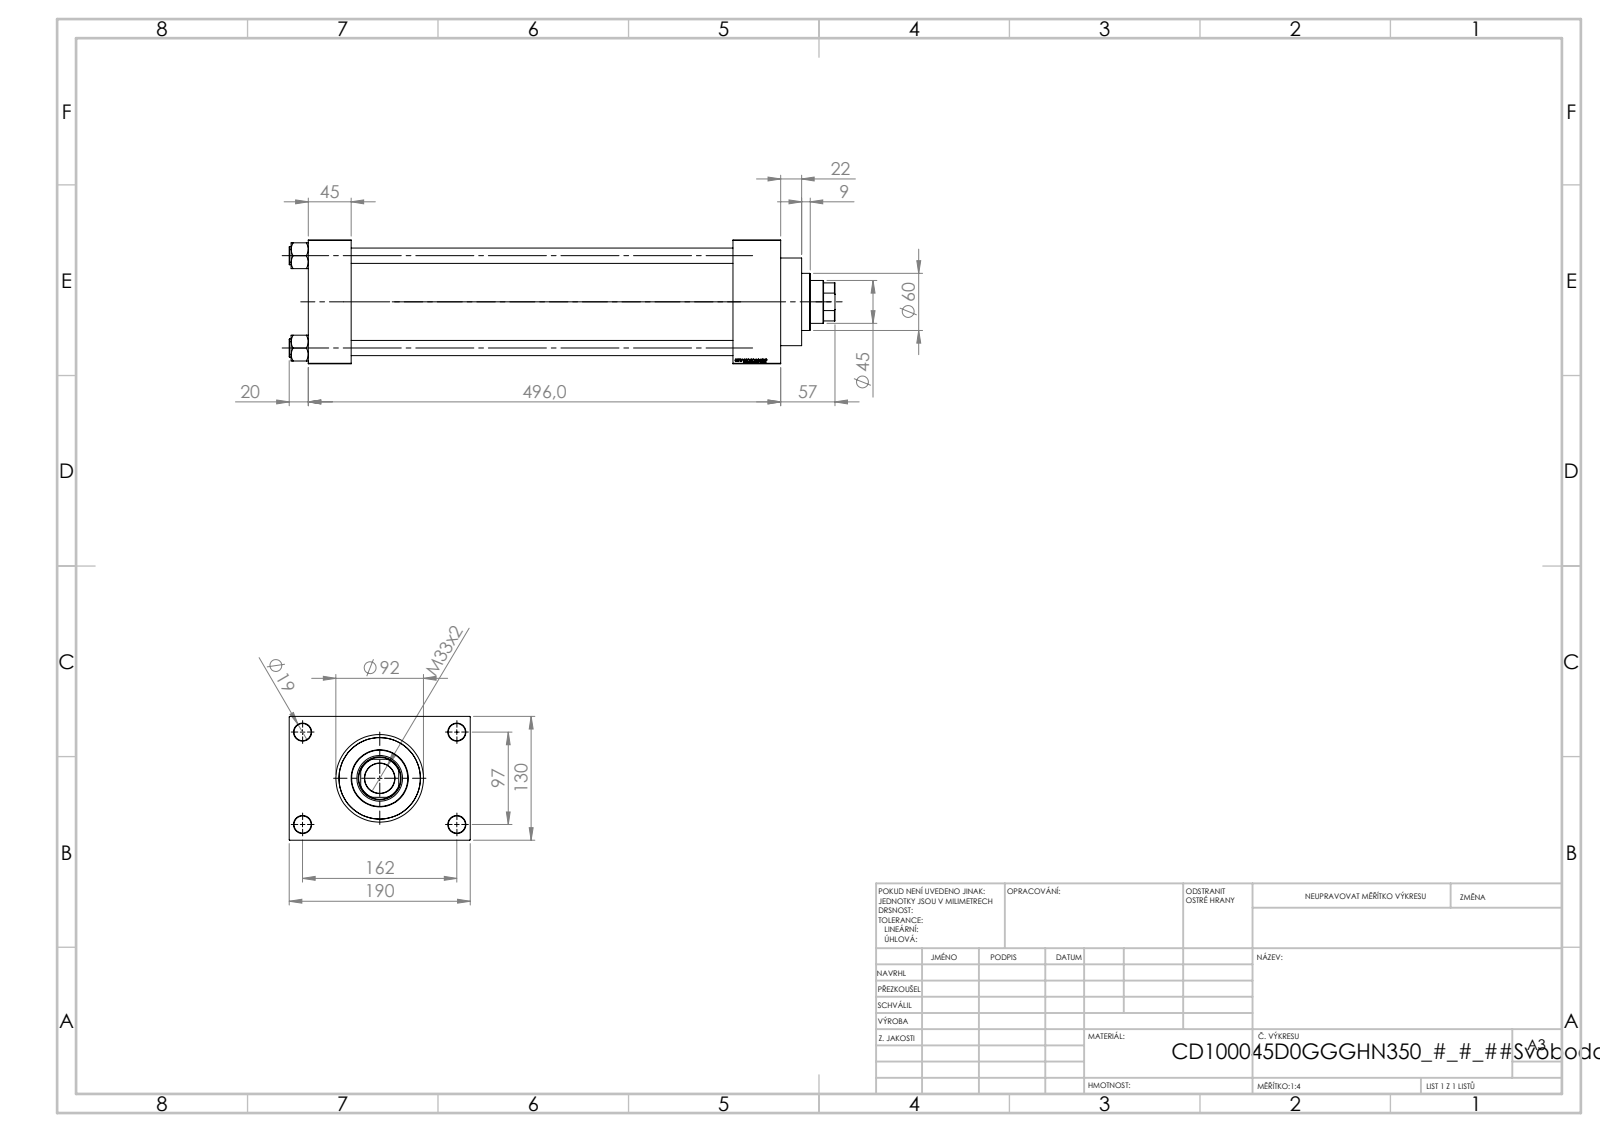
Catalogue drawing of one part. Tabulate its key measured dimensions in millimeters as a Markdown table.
| quantity | value |
| --- | --- |
| part name | V215CD_VCP_D; V215CD_D_Body; V215CD_VC_A; V215CD_D_TYCINKA (+1 more) |
| STEP written by | SolidWorks 2019 (CONFIG_CONTROL_DESIGN) |
| units | millimeters |
| bodies | 11 solids, 1152 faces (545 planar, 89 cylindrical, 518 other) |
| overall size | 573 × 190 × 130 |
| volume | 3 717 000 mm³ |
| surface area | 678 962 mm² |
| round holes (diameter × count) | 16 × 4, 18 × 4, 7 × 2, 26.44 × 2, 35 × 2, 31.5 × 1, 45 × 1, 48 × 1, 76 × 1, 85.5 × 1, 100 × 1 |
| round bosses / shafts (diameter × count) | 19 × 4, 106 × 1, 92 × 1, 60 × 1 |
| partial cylindrical surfaces (radius × count) | 22 × 1 |
| main face-to-face distances | 130, 45, 446, 401, 496, 451, 50, 30, 160, 190 |
| hole center spacings | 32.55, 68.52, 94.41, 96.9, 102.27, 129.45, 161.73, 97 |
